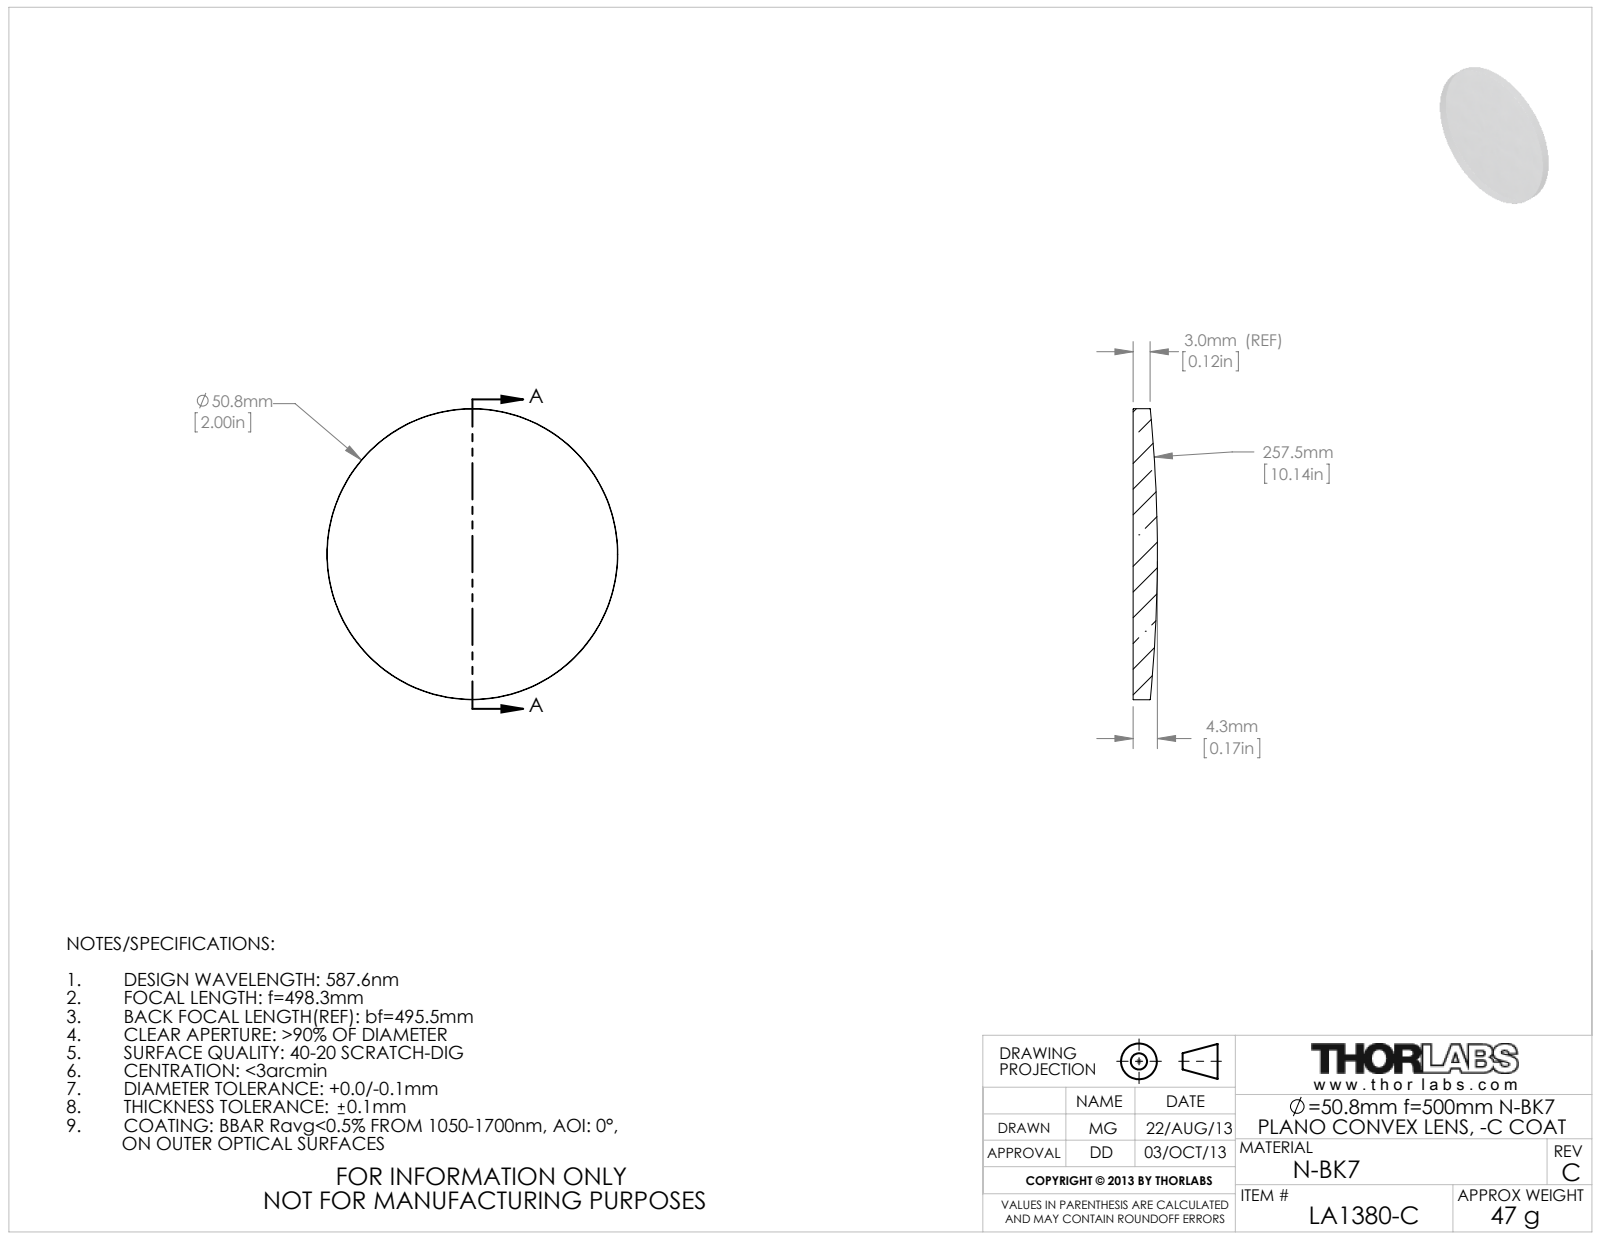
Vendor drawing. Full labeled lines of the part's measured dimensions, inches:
Part name (STEP PRODUCT): 4610-E0W
STEP written by: SolidWorks 2009 (AUTOMOTIVE_DESIGN)
Units: inches
Bodies: 0 solids, 5 faces (1 planar, 2 cylindrical, 2 other)
Overall size (bounding box): 2 × 2 × 0.167
Round bosses / shafts (diameter × count): ⌀2 ×1
